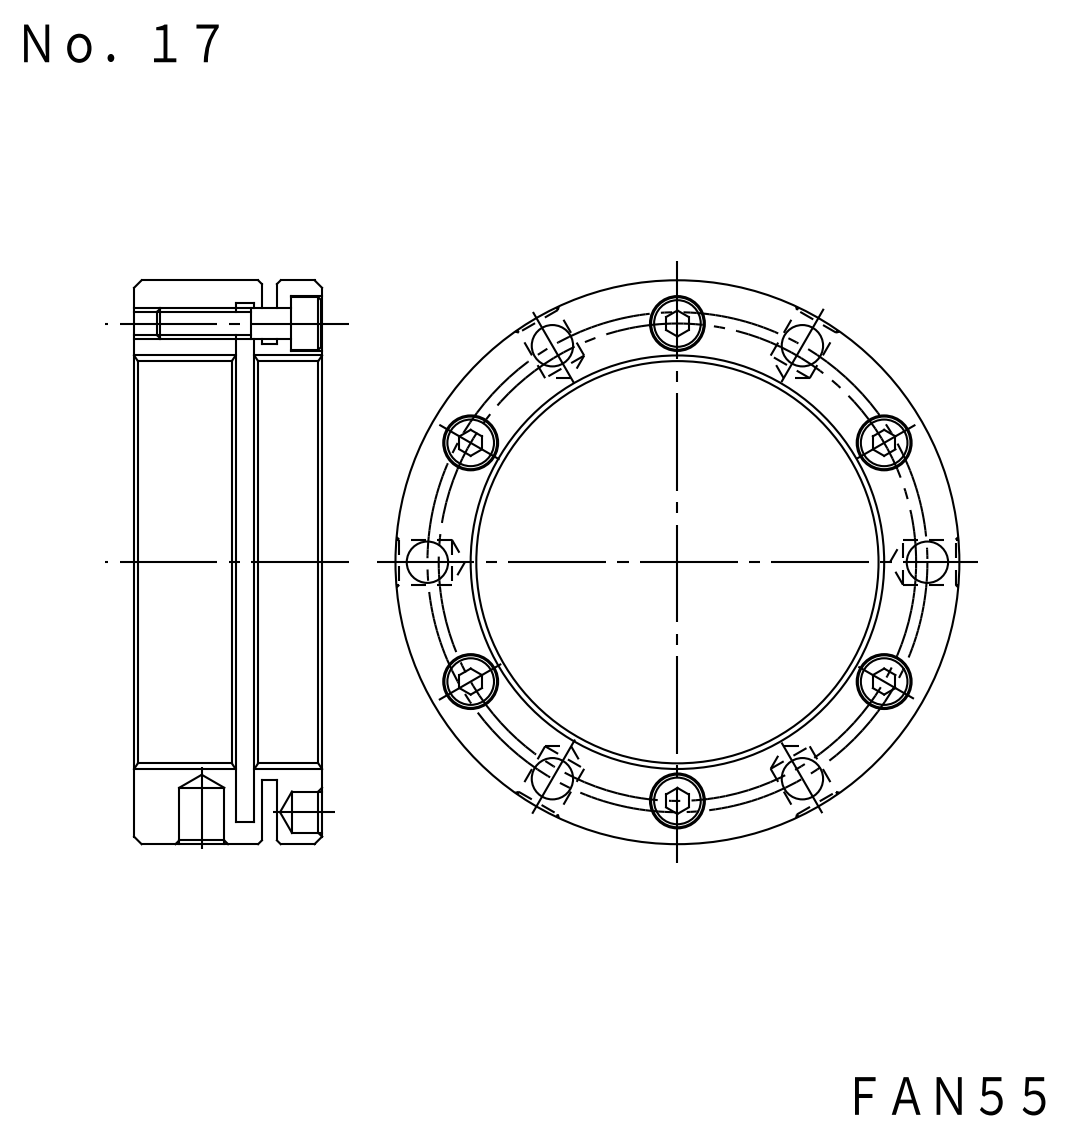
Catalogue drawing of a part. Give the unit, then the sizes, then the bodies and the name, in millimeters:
Units: millimetres
Overall size (bounding box): 75 × 75 × 25
Round holes (diameter × count): ⌀3.24 ×6, ⌀4.3 ×6, ⌀4.5 ×6, ⌀7.3 ×6, ⌀6 ×3, ⌀55 ×1, ⌀70 ×1
Round bosses / shafts (diameter × count): ⌀7 ×6, ⌀4 ×6, ⌀75 ×1, ⌀60 ×1
Main face-to-face distances: 6, 25, 4, 2, 17, 19, 8, 13, 12, 15.5
Hole centre spacings: 32.5, 46.5, 17.04, 33.25, 63.51, 63.52, 17.03, 33.26
Volume: 42 707 mm³ · Surface area: 25 233 mm²
Bodies: 7 solids, 204 faces (72 planar, 108 cylindrical, 24 other)
Part name (STEP PRODUCT): FKD FAN55; M4X18_default
STEP written by: SolidWorks 2012 (CONFIG_CONTROL_DESIGN)
